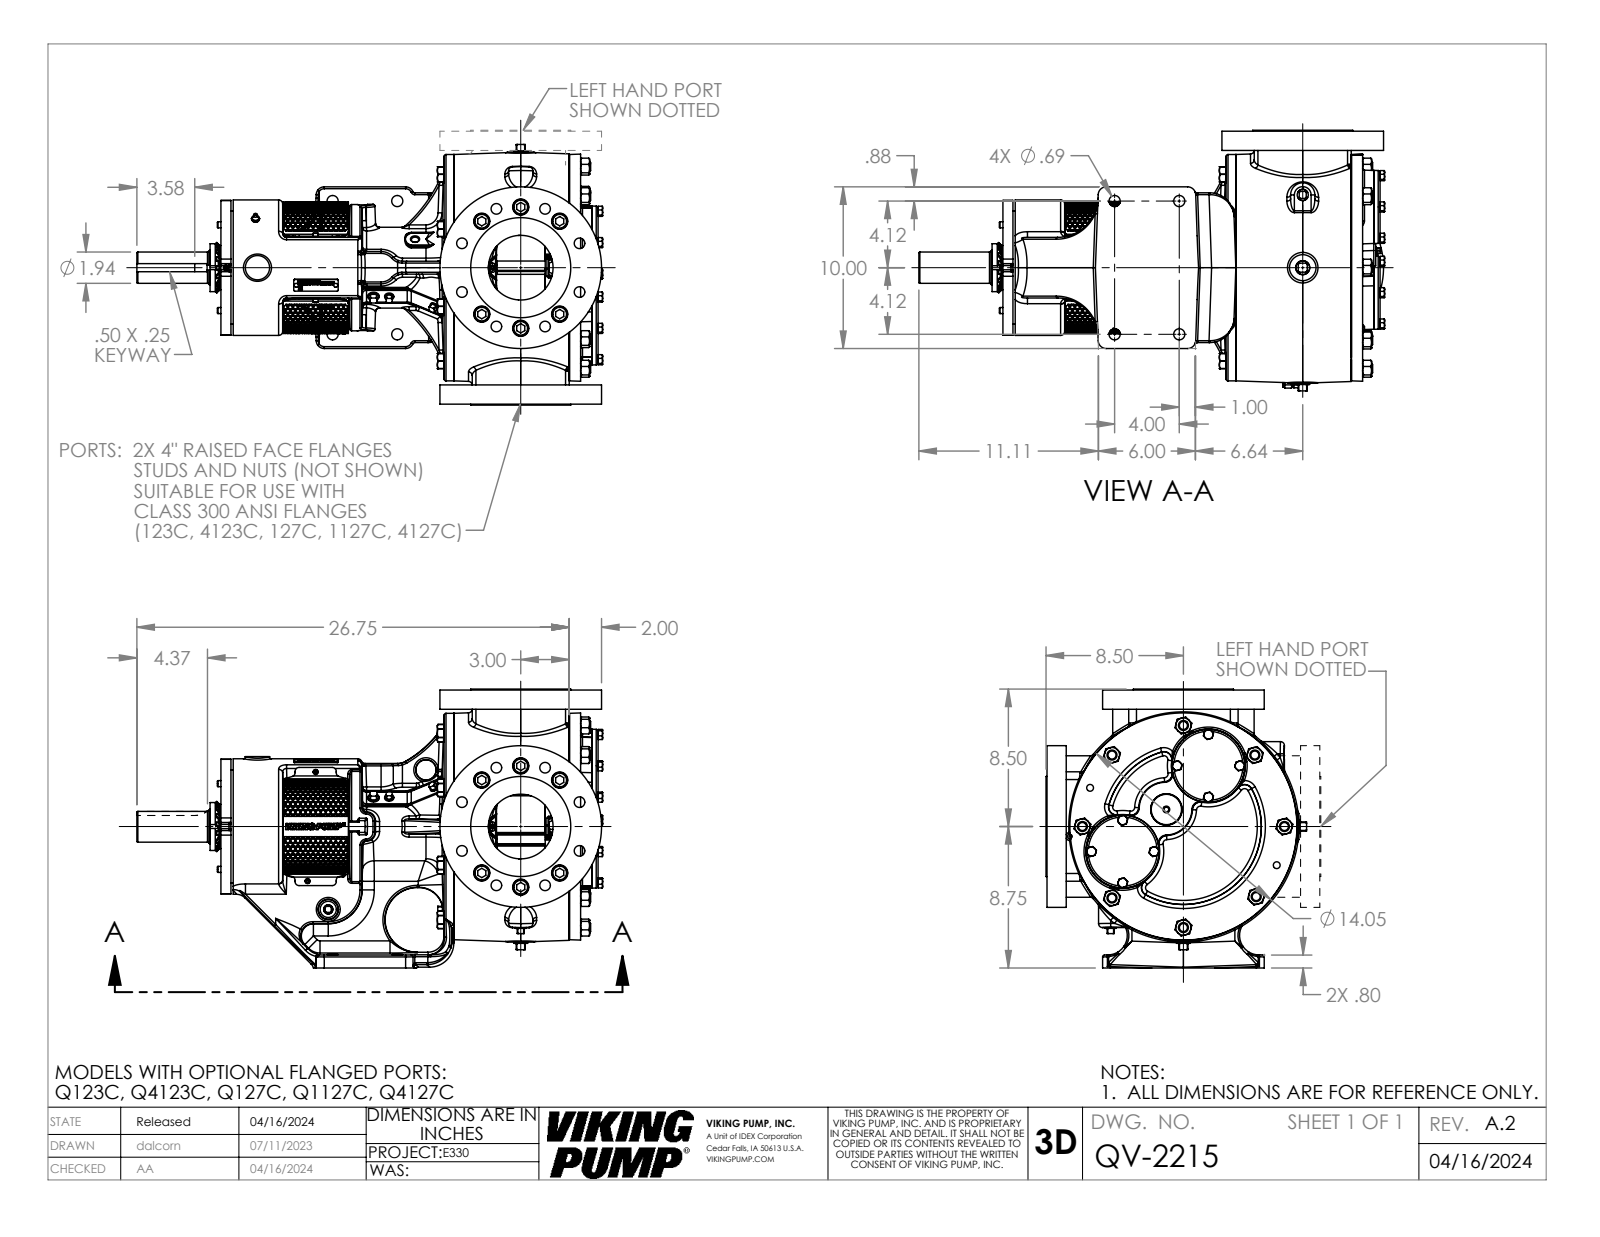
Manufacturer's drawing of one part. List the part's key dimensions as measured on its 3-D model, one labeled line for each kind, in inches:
Part name (STEP PRODUCT): QV-2215
STEP written by: SolidWorks 2022 (AUTOMOTIVE_DESIGN)
Units: inches
Bodies: 1 solid, 4104 faces (1475 planar, 719 cylindrical, 1910 other)
Overall size (bounding box): 28.814 × 17.25 × 16.121
Volume: 2 130 in³ · Surface area: 2 167 in²
Round holes (diameter × count): ⌀0.656 ×16, ⌀1 ×12, ⌀0.25 ×9, ⌀0.266 ×8, ⌀0.406 ×8, ⌀0.41 ×8, ⌀1.157 ×8, ⌀0.688 ×4, ⌀0.159 ×2, ⌀0.313 ×2, ⌀0.33 ×2, ⌀0.422 ×2
Round bosses / shafts (diameter × count): ⌀0.937 ×12, ⌀0.617 ×8, ⌀0.375 ×8, ⌀0.312 ×3, ⌀0.19 ×3, ⌀10 ×2, ⌀6.19 ×2, ⌀4.5 ×2
Partial cylindrical surfaces — rounded edges, fillets, slot ends (radius × count): R0.12 ×60, R0.25 ×30, R0.015 ×18, R0.092 ×18, R0.07 ×16, R0.75 ×16, R0.5 ×15, R0.06 ×8
Main face-to-face distances: 1.19, 3.75, 16, 1.25, 17.19, 0.5, 0.06, 21.756, 22.256, 18.006
Hole centre spacings: 3.75, 7.276, 2.079, 3.937, 5.783, 1.184, 2.713, 3.013
